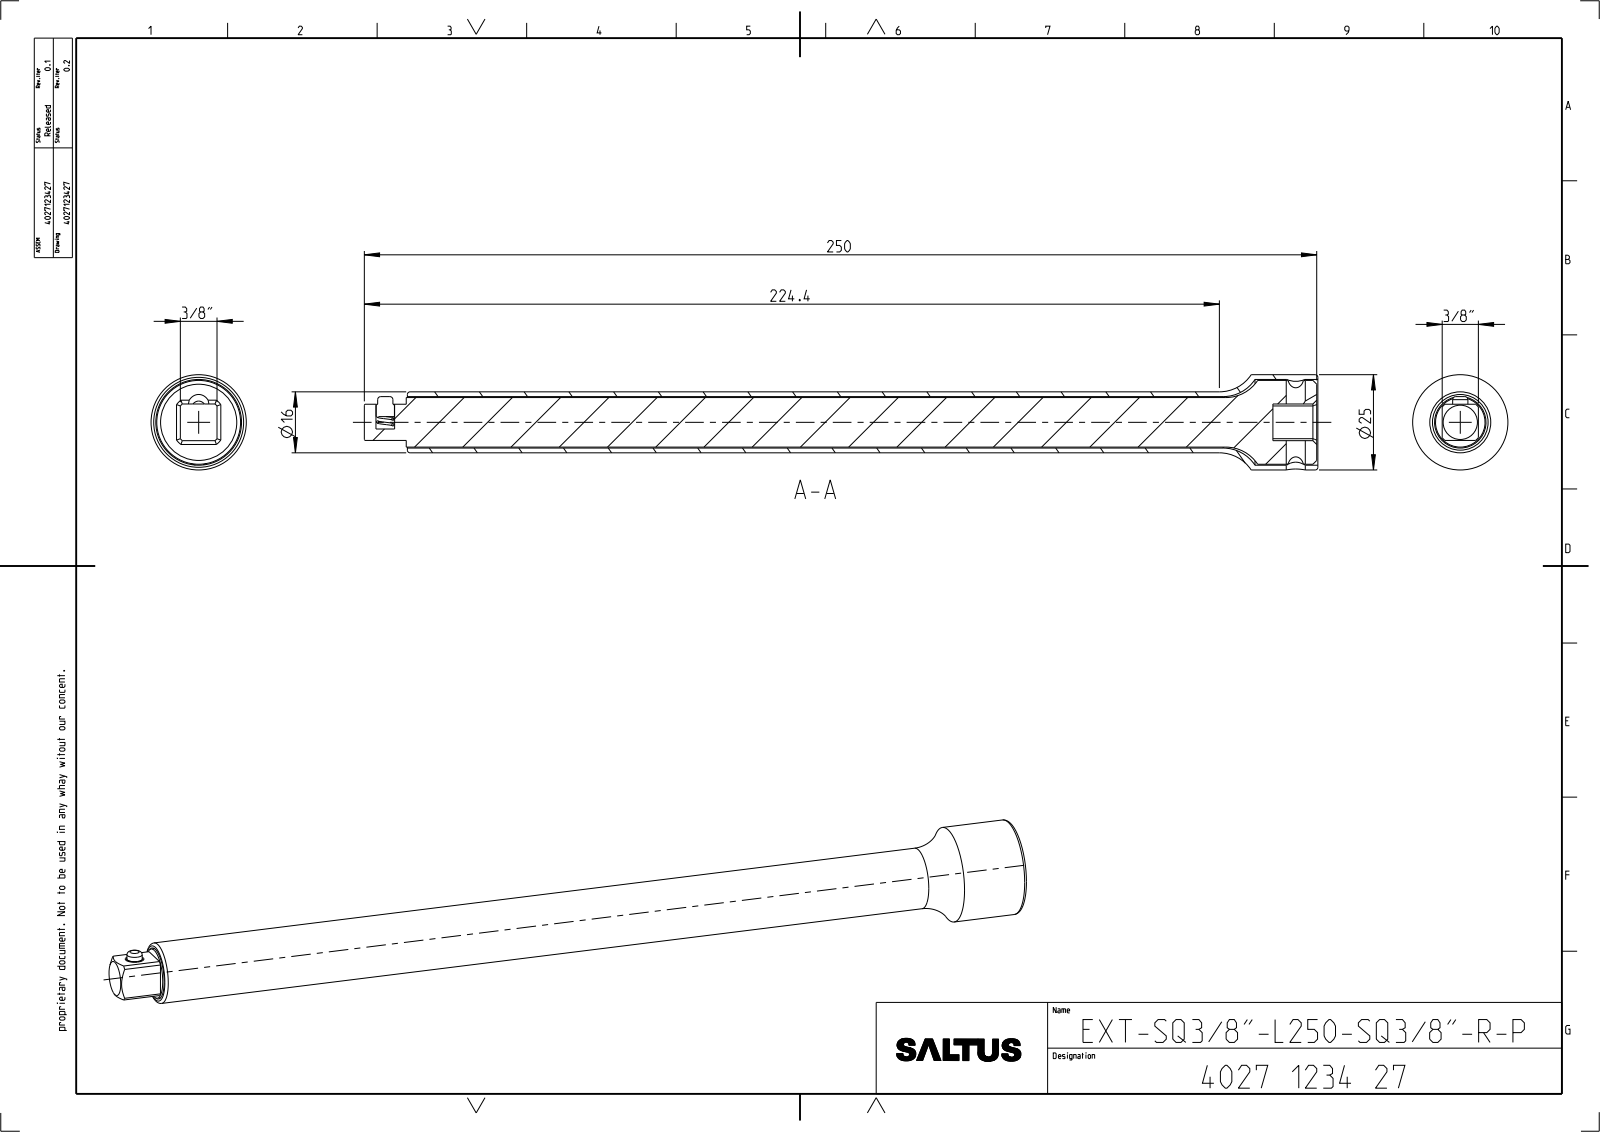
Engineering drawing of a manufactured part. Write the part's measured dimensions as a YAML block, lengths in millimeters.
part_name: "4027123407; 4027040475; 4027123427_ASM"
step_written_by: "CREO PARAMETRIC BY PTC INC, 2022414 (CONFIG_CONTROL_DESIGN)"
units: millimeters
bodies: {solids: 3, faces: 88, planar: 24, cylindrical: 37, other: 27}
overall_size: [250.3, 25, 25]
volume: 50277
surface_area: 35557
round_holes:
  - {diameter: 4.9, count: 1}
  - {diameter: 5, count: 1}
  - {diameter: 13.5, count: 1}
  - {diameter: 22.5, count: 1}
round_bosses_or_shafts:
  - {diameter: 25, count: 1}
  - {diameter: 22, count: 1}
  - {diameter: 16, count: 1}
  - {diameter: 13, count: 1}
  - {diameter: 4.8, count: 1}
  - {diameter: 4, count: 1}
partial_cylinders:
  - {radius: 3, count: 1}
  - {radius: 6.22, count: 1}
  - {radius: 6.45, count: 1}
face_to_face_distances: [9.56, 9.5, 9.62, 11.5, 239, 250, 238.5, 227.5, 11, 11.8]
hole_center_spacings: [239]
